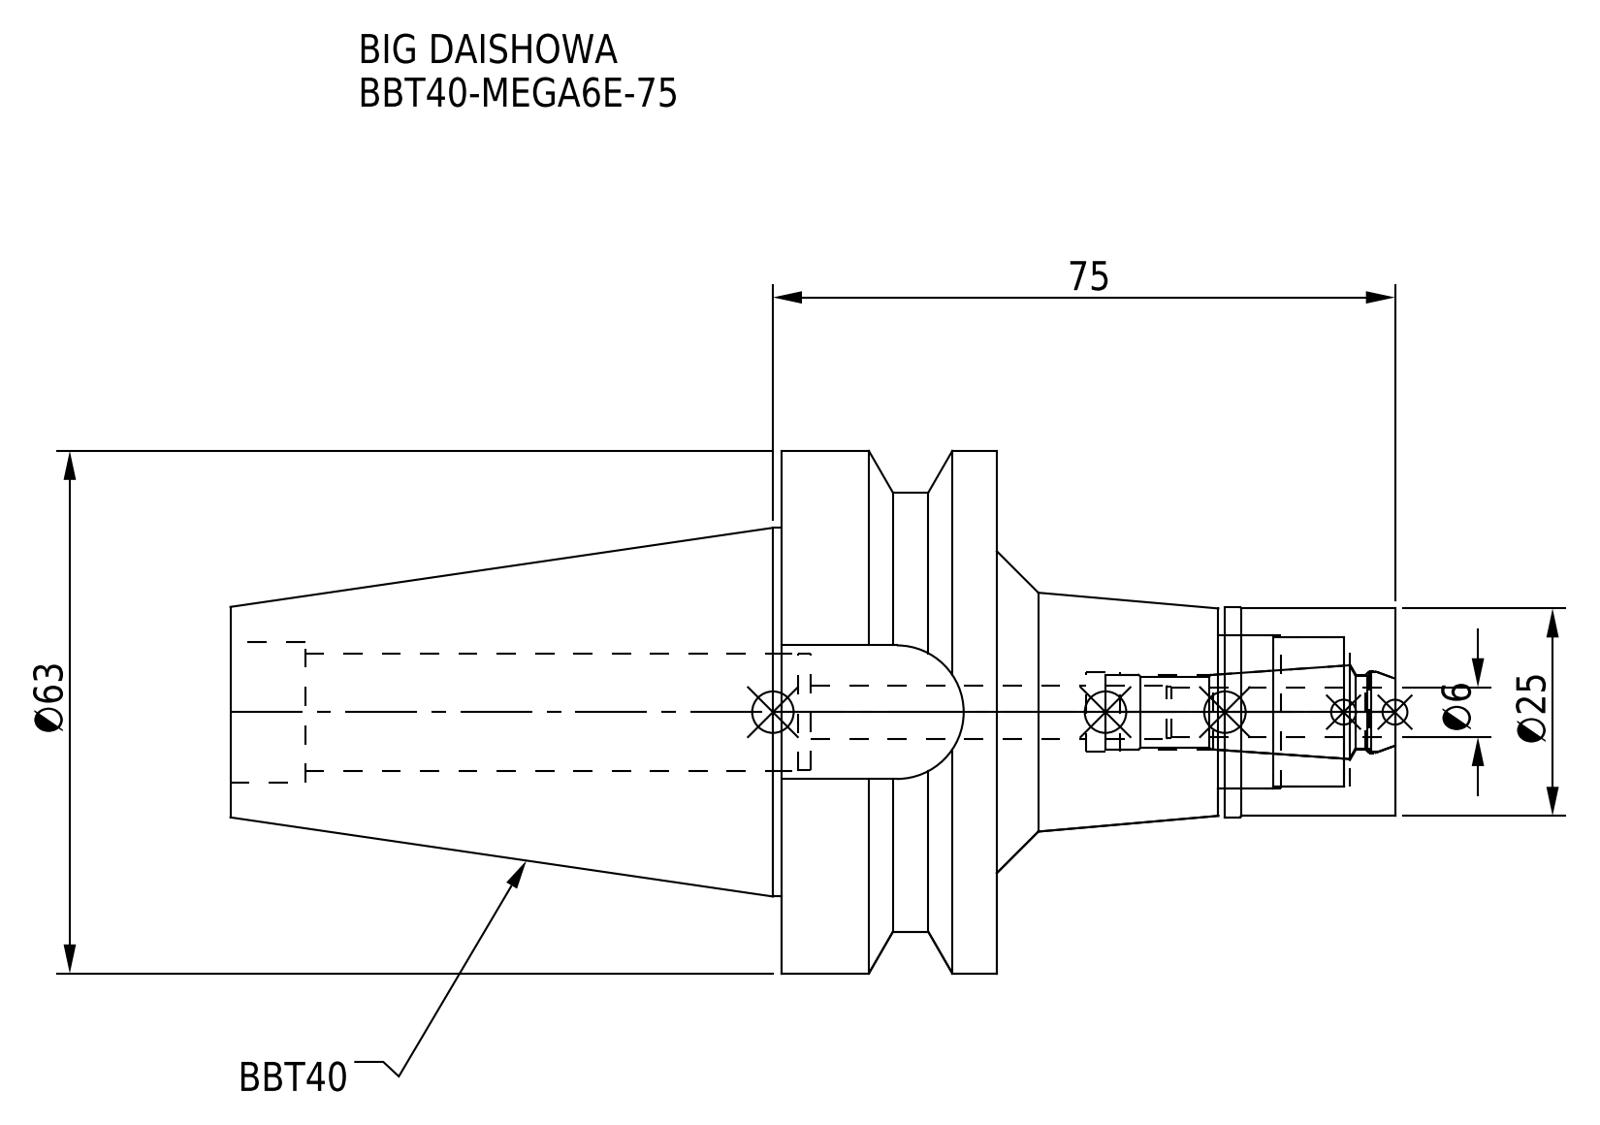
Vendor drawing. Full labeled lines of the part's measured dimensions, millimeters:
Part name (STEP PRODUCT): MEN6_1.stp; BBT40ME06075-060_ASM.stp; DXF_TEMP_ASSY_ASM_4_ASM.stp; BBT40-MEGA6E-75-060-FreeParts (+3 more)
STEP written by: SolidWorks 2019 (CONFIG_CONTROL_DESIGN)
Units: millimetres
Bodies: 2 solids, 81 faces (21 planar, 40 cylindrical, 20 other)
Overall size (bounding box): 140.4 × 63 × 63
Volume: 147 143 mm³ · Surface area: 29 809 mm²
Round holes (diameter × count): ⌀6.4 ×1, ⌀9 ×1, ⌀9.6 ×1, ⌀9.9 ×1, ⌀14 ×1, ⌀14.2 ×1, ⌀17 ×1, ⌀18 ×1, ⌀18.5 ×1
Round bosses / shafts (diameter × count): ⌀63 ×1, ⌀53 ×1, ⌀44.45 ×1, ⌀25.3 ×1, ⌀25 ×1
Partial cylindrical surfaces — rounded edges, fillets, slot ends (radius × count): R8.05 ×1
Main face-to-face distances: 26, 48, 74, 45, 140.4, 92.4, 66.4, 20.5, 27.5, 53.5
